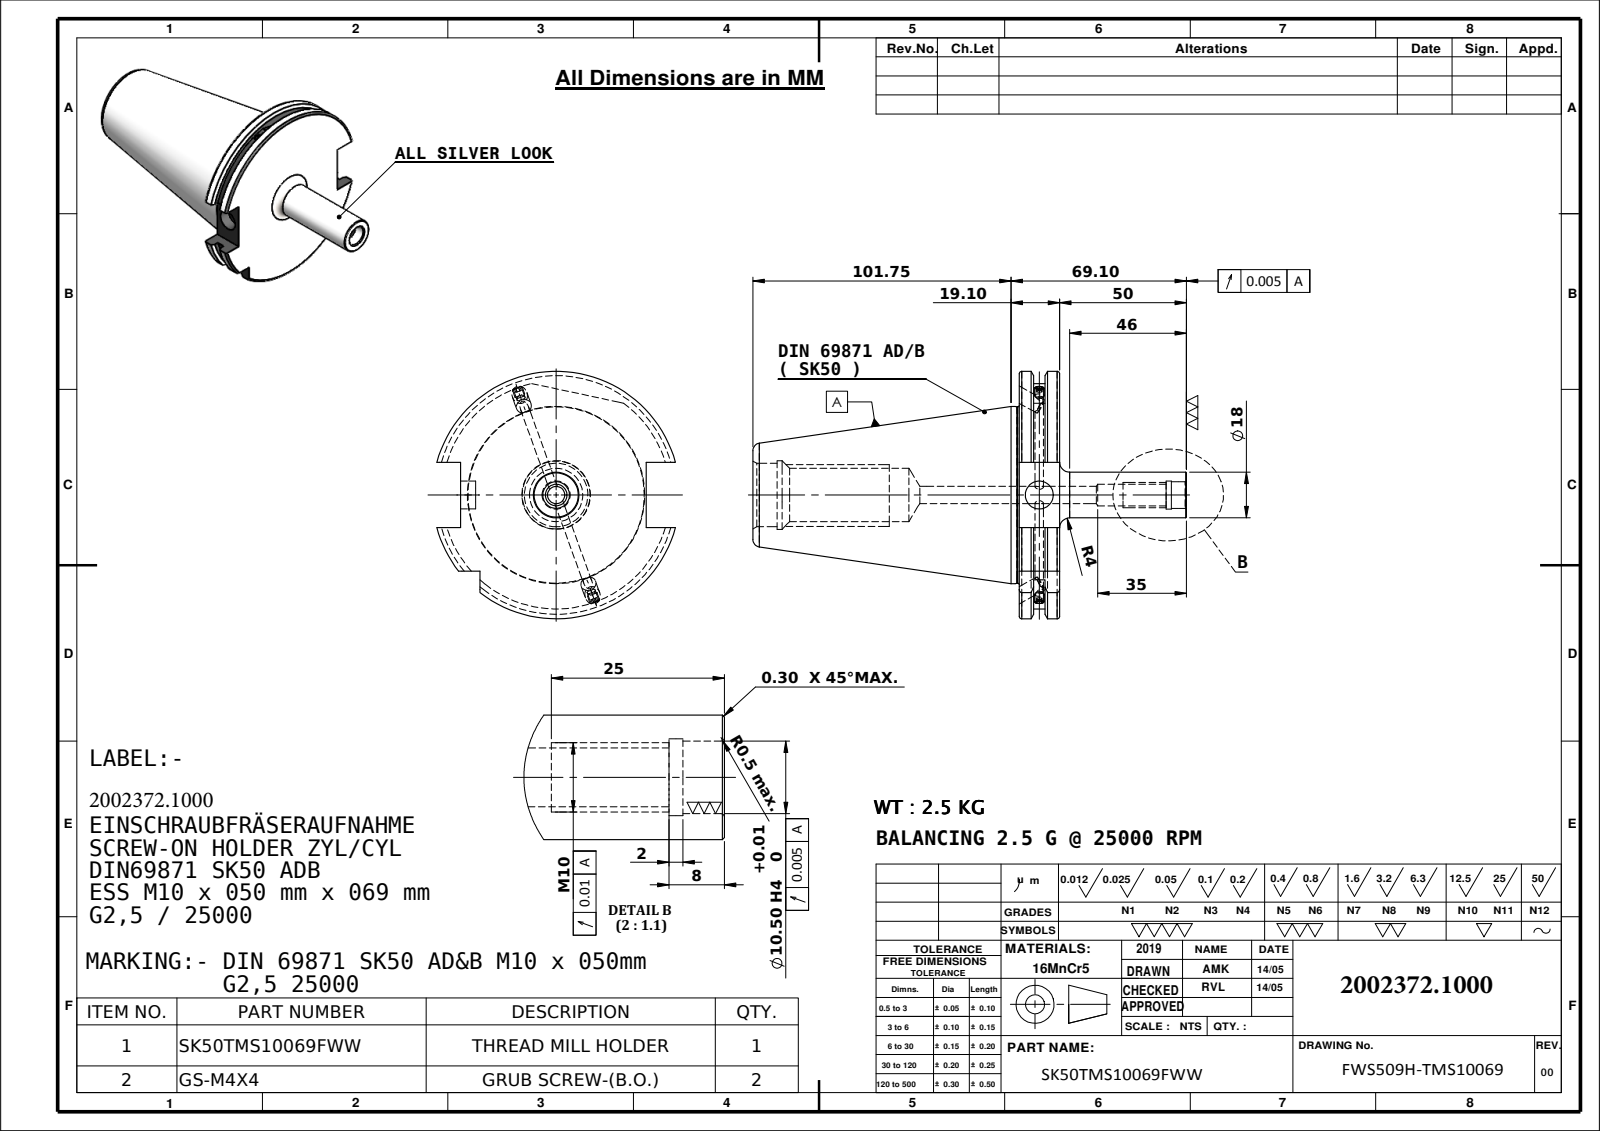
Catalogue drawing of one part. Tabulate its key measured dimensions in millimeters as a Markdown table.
| quantity | value |
| --- | --- |
| part name | 91506-ESS7M10050 |
| STEP written by | SolidWorks 2018 (CONFIG_CONTROL_DESIGN) |
| units | millimeters |
| bodies | 1 solid, 112 faces (25 planar, 47 cylindrical, 40 other) |
| overall size | 170.85 × 97.5 × 94.05 |
| volume | 345 571 mm³ |
| surface area | 46 949 mm² |
| round holes (diameter × count) | 6 × 2, 3.3 × 1, 6.8 × 1, 8.5 × 1, 10.5 × 1, 11 × 1, 11.1 × 1, 21 × 1, 25 × 1, 27 × 1 |
| round bosses / shafts (diameter × count) | 69.85 × 1, 69.45 × 1, 18 × 1 |
| partial cylindrical surfaces (radius × count) | 44.9 × 1, 48.75 × 1 |
| main face-to-face distances | 15.9, 5.66, 10.24, 10.14, 4.48, 5.76, 104.95, 110.61, 115.09, 120.85 |
